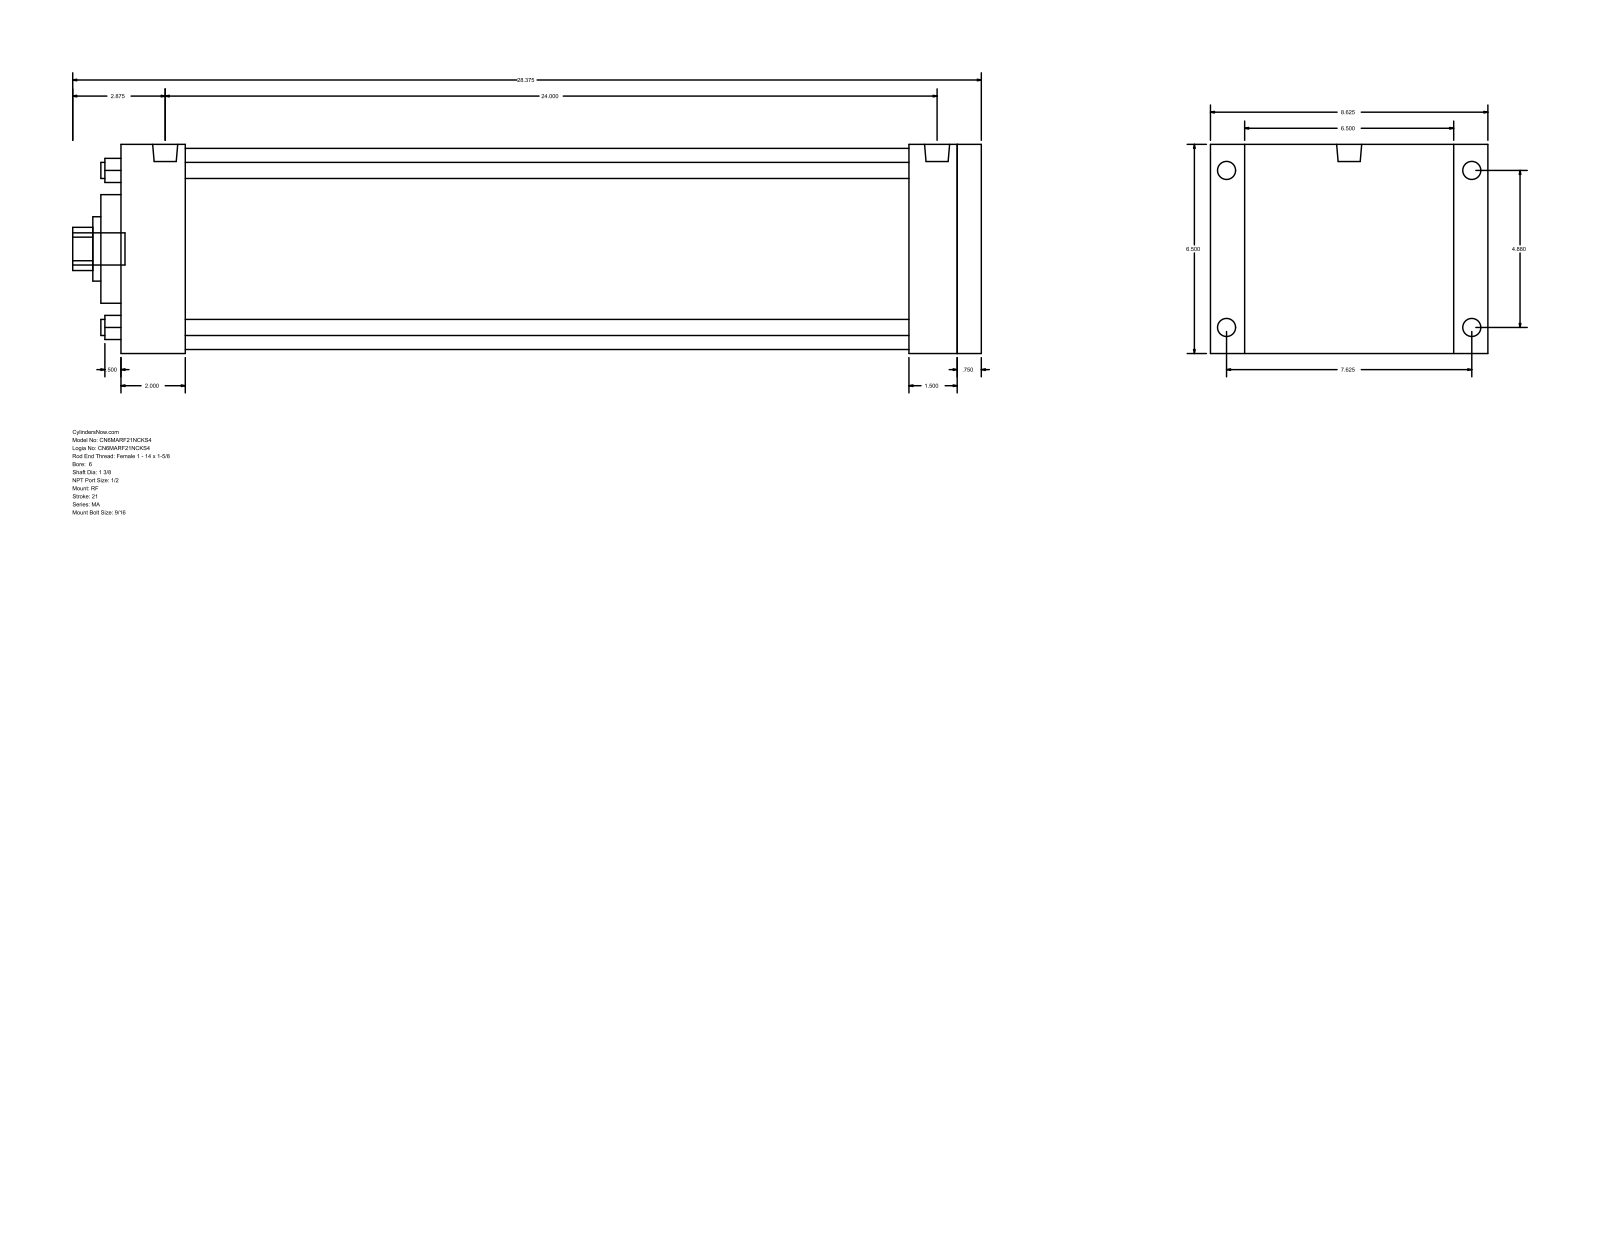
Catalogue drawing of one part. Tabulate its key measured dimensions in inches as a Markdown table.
| quantity | value |
| --- | --- |
| part name | MA_RF__0600_1.375 |
| STEP written by | GSSL Pune (CONFIG_CONTROL_DESIGN) |
| units | inches |
| bodies | 0 solids, 94 faces (65 planar, 29 cylindrical, 0 other) |
| overall size | 28.375 × 8.625 × 6.5 |
| round holes (diameter × count) | 0.5 × 4, 1.375 × 1, 2 × 1, 3.375 × 1, 6.25 × 1 |
| round bosses / shafts (diameter × count) | 0.687 × 4, 0.563 × 4, 0.778 × 2, 1 × 1 |
| partial cylindrical surfaces (radius × count) | 0.672 × 1 |
| main face-to-face distances | 6.5, 26.875, 26.125, 0.75, 2, 24.125, 24.875, 24.625, 22.625, 1.5 |
| hole center spacings | 3.451, 4.88, 6.902 |
